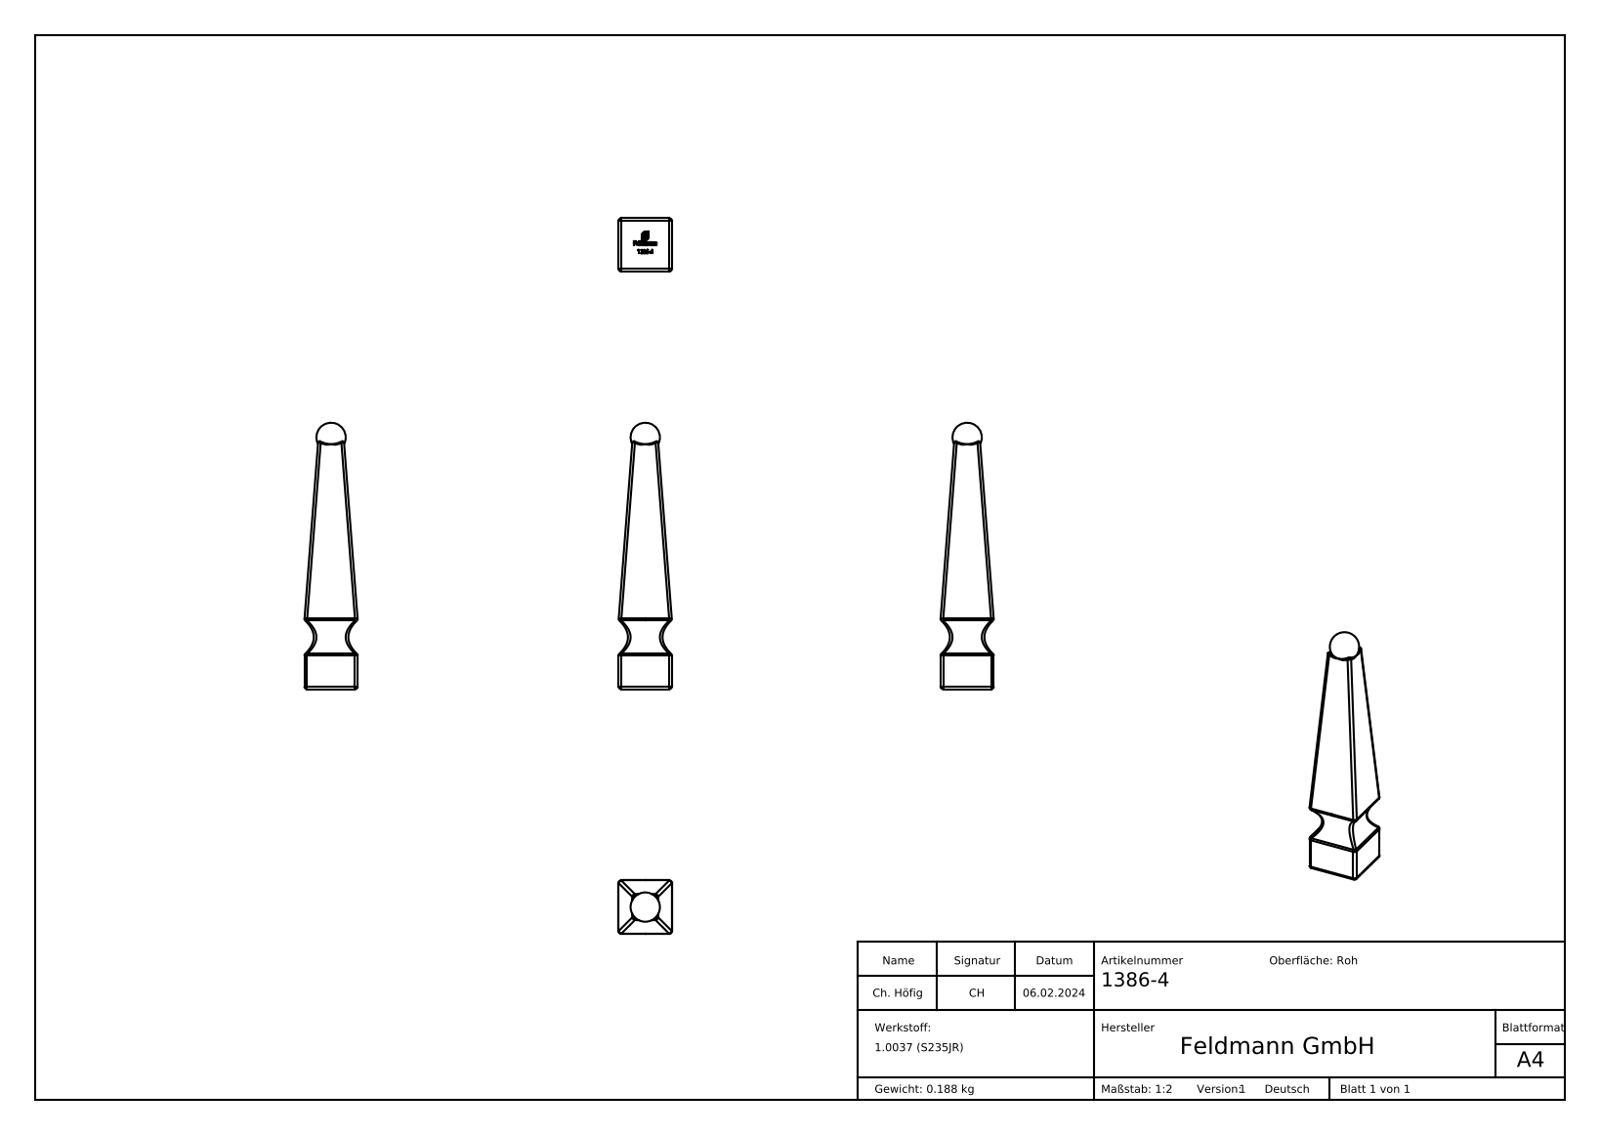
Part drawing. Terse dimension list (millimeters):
name: 1386-4
written by: SolidWorks 2018 (CONFIG_CONTROL_DESIGN)
unit: mm
bodies: 1 solid, 323 faces (136 planar, 20 cylindrical, 167 other)
size: 100 × 20 × 20
volume: 24 048 mm³; area: 6 445 mm²
rounds: 12× R1, 2× R8.43
face distances: 20, 1.14, 2.01, 3.27, 1.26, 0.34, 10, 8.99, 11.01, 1.38
